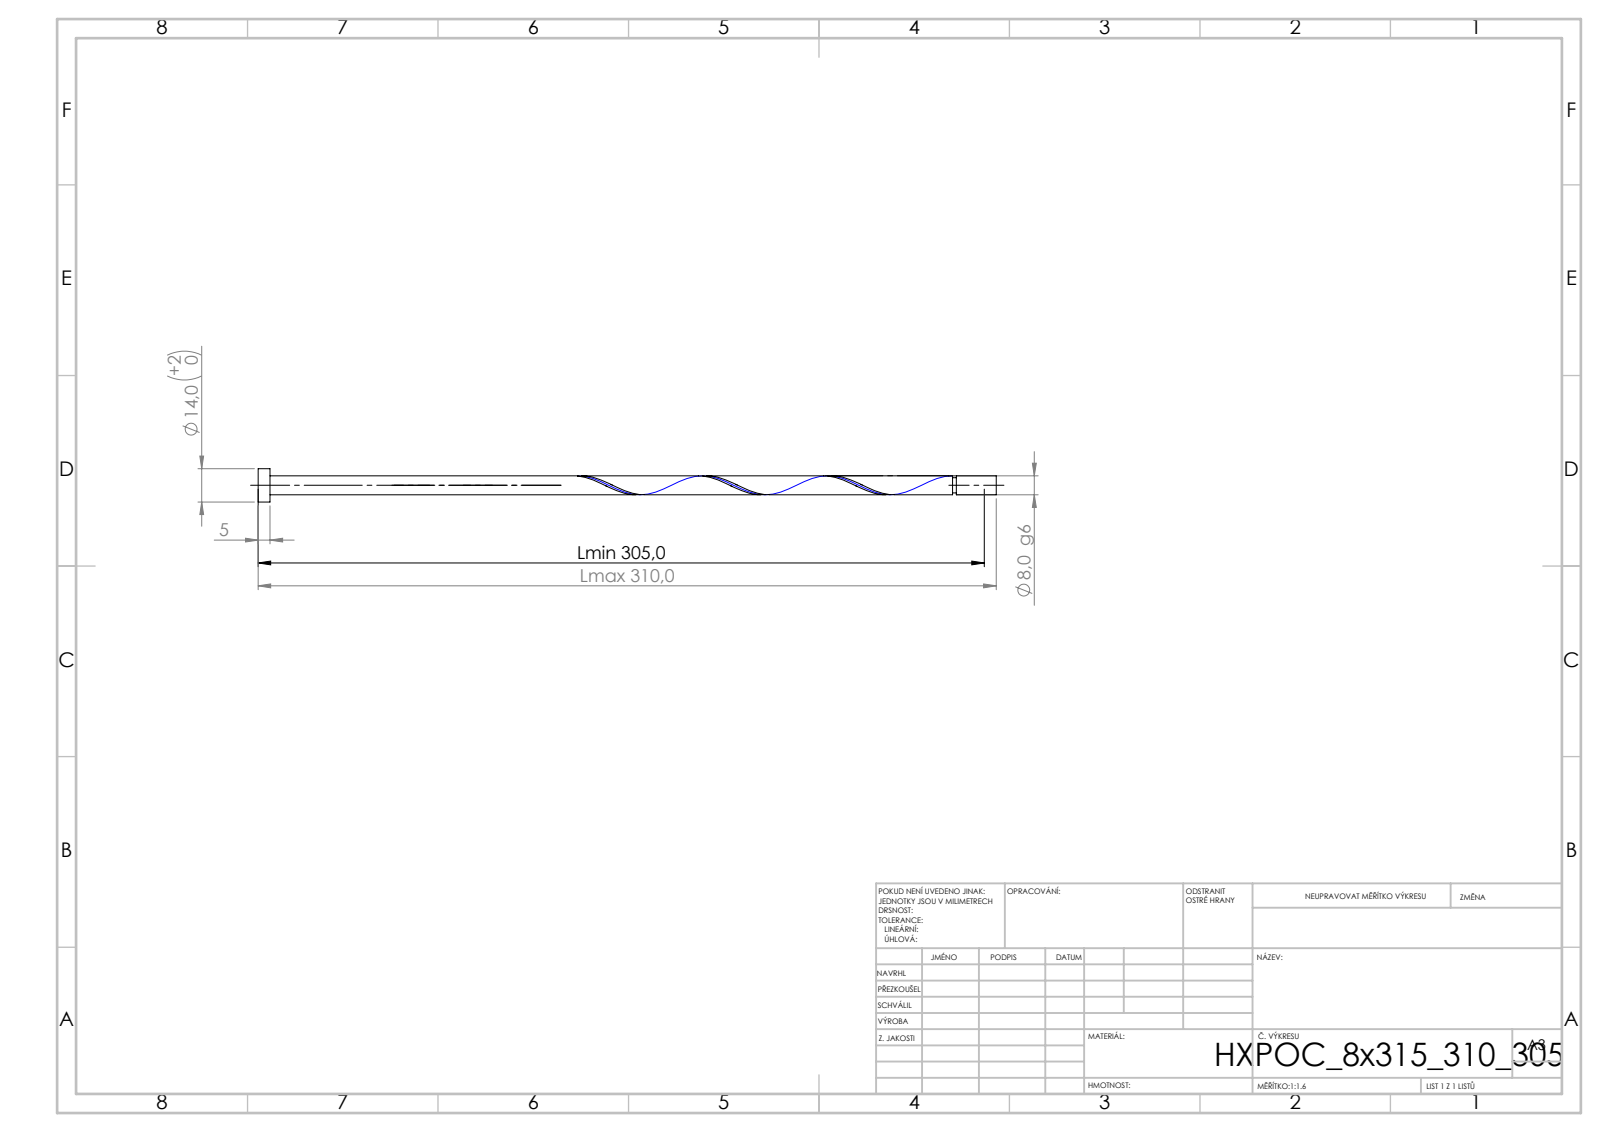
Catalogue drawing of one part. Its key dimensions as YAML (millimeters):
step_written_by: "SolidWorks 2019 (CONFIG_CONTROL_DESIGN)"
units: millimeters
bodies: {solids: 1, faces: 21, planar: 6, cylindrical: 14, other: 1}
overall_size: [310, 14, 14]
volume: 15920
surface_area: 8359
round_bosses_or_shafts:
  - {diameter: 14, count: 1}
  - {diameter: 8, count: 1}
  - {diameter: 6.4, count: 1}
face_to_face_distances: [5, 310, 305, 293.26, 288.26, 16.74, 291.66, 286.66, 1.6, 18.34]
